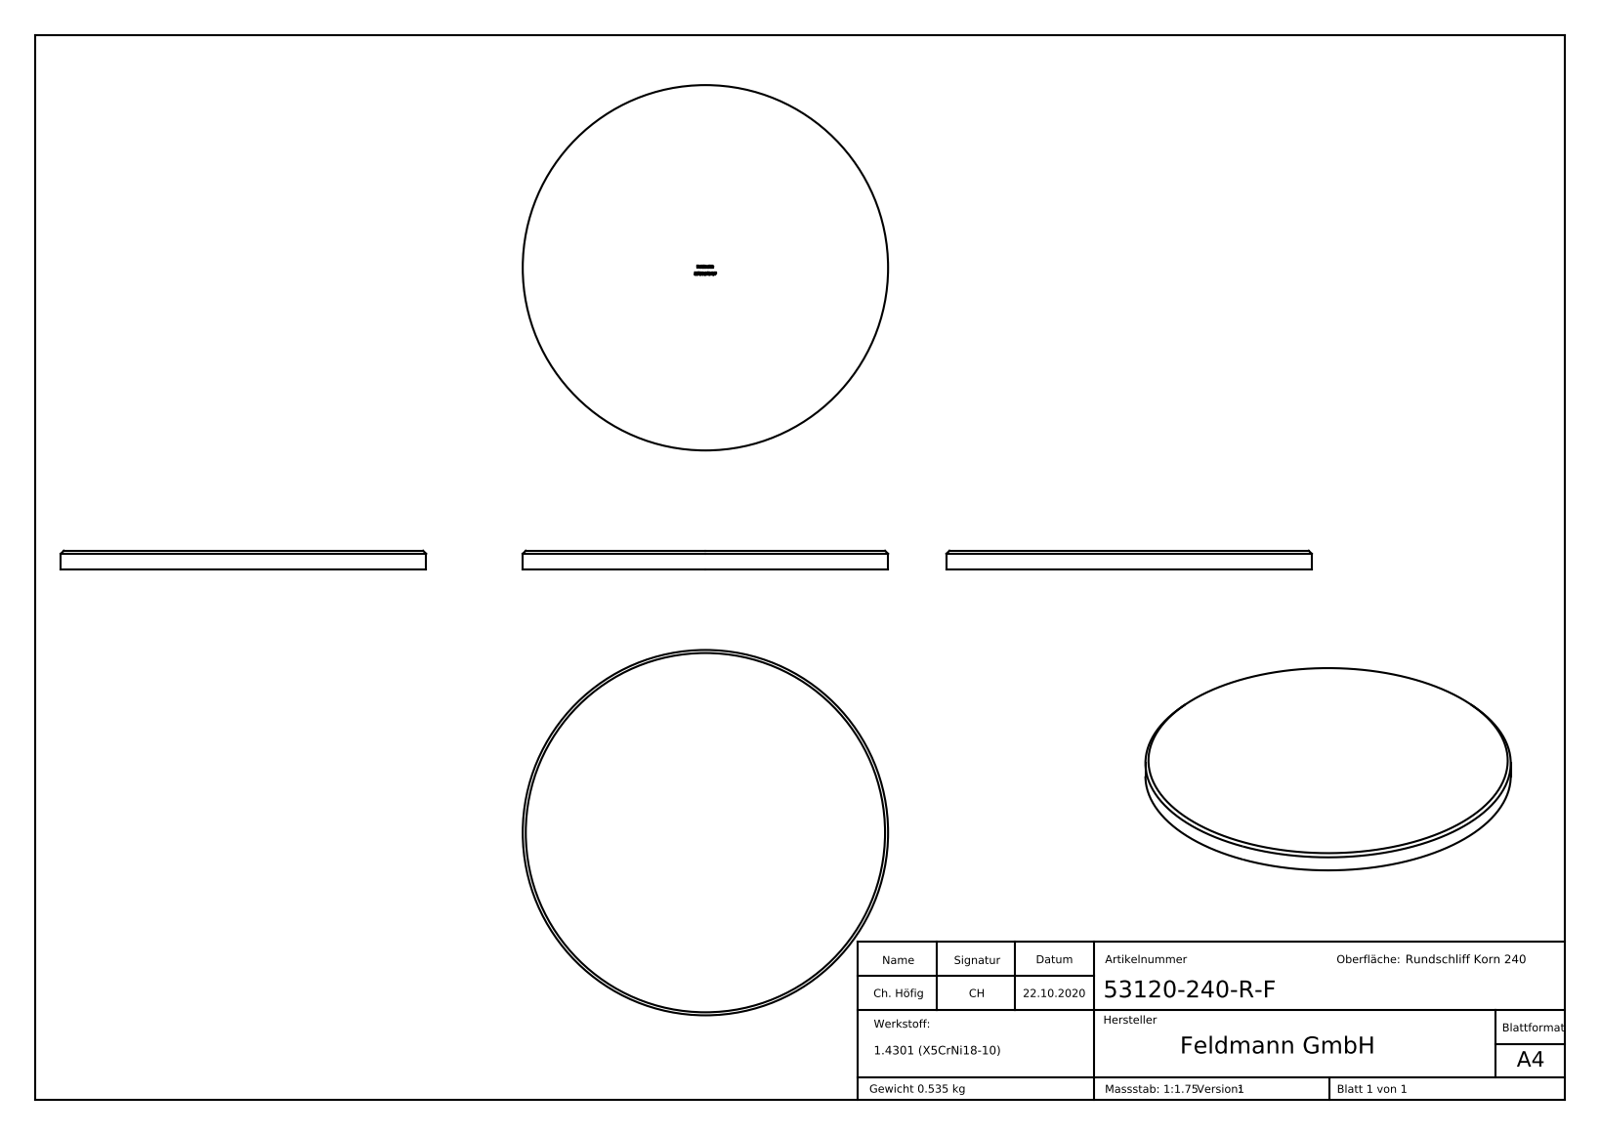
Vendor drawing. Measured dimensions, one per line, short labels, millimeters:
name: 53120-240-R-F
written by: SolidWorks 2018 (CONFIG_CONTROL_DESIGN)
unit: mm
bodies: 1 solid, 266 faces (157 planar, 2 cylindrical, 107 other)
size: 120 × 120 × 6
volume: 67 671 mm³; area: 24 666 mm²
bosses: 1× ⌀120
face distances: 6, 5.9, 2.32, 1.21, 0.79, 2.24, 3.49, 0.47, 0.71, 1.78
